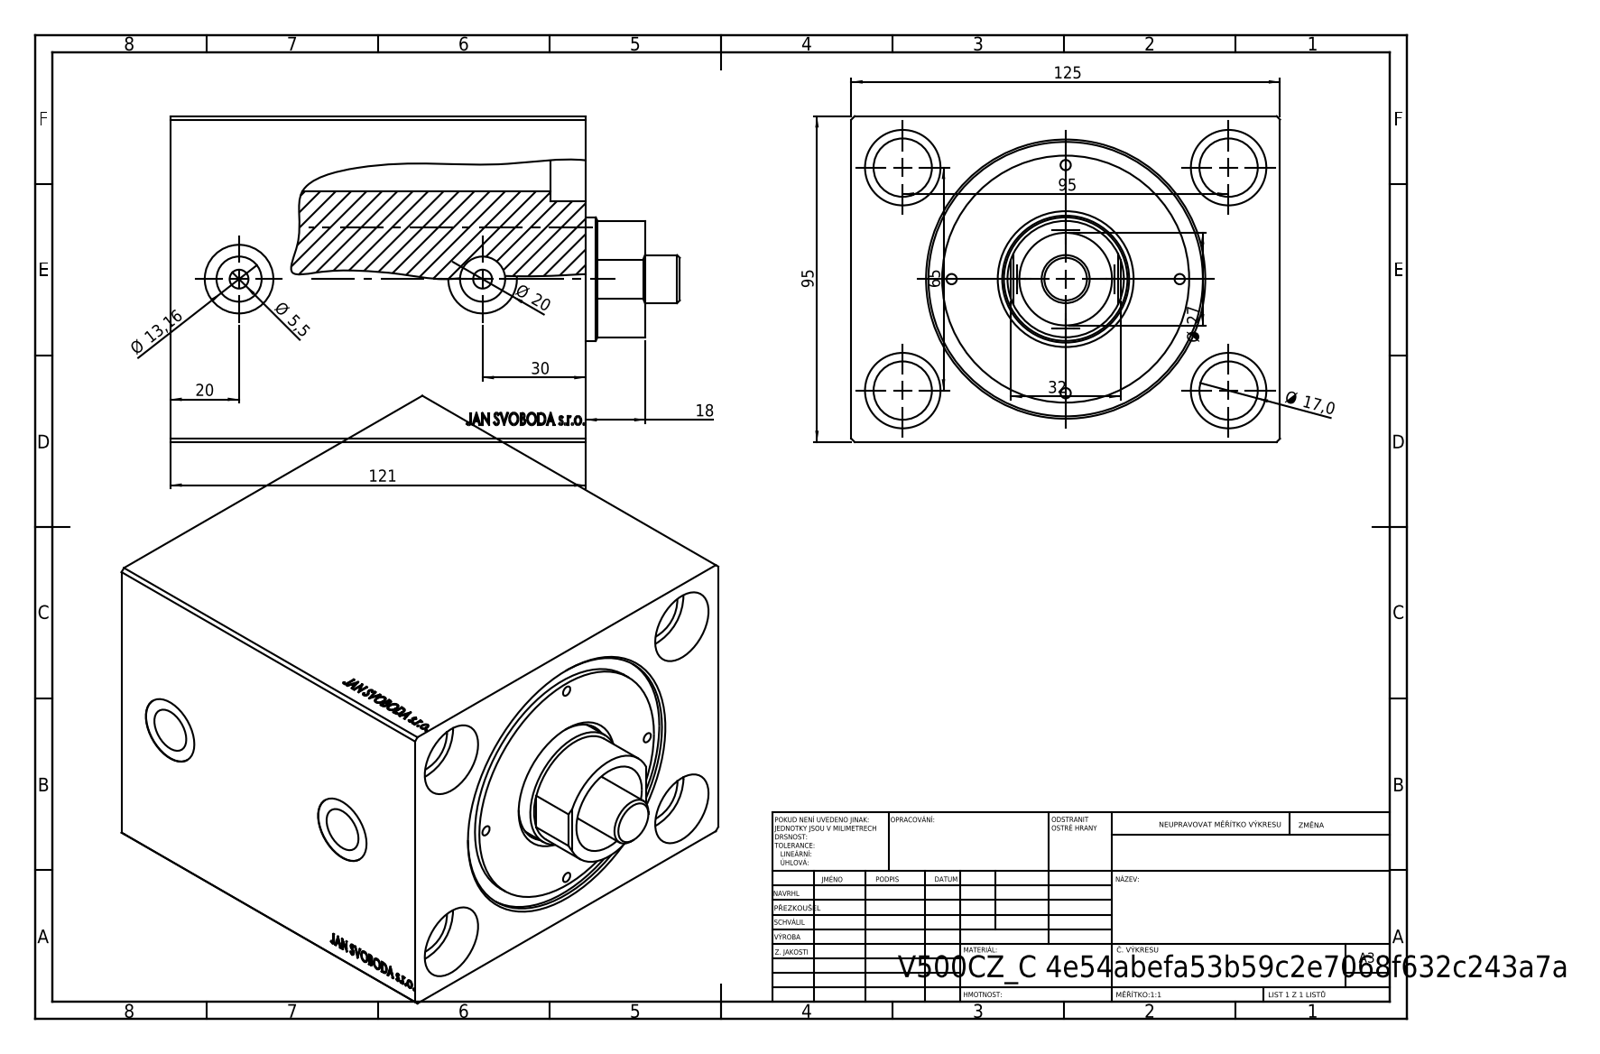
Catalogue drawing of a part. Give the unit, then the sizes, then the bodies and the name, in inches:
Units: inches
Overall size (bounding box): 5.846 × 4.921 × 3.74
Round holes (diameter × count): ⌀0.118 ×4, ⌀0.669 ×4, ⌀0.866 ×4, ⌀0.217 ×2, ⌀0.518 ×2, ⌀0.787 ×2, ⌀1.063 ×1, ⌀1.417 ×1, ⌀1.457 ×1, ⌀2.48 ×1, ⌀3.15 ×1
Round bosses / shafts (diameter × count): ⌀2.835 ×1, ⌀0.551 ×1, ⌀0.472 ×1
Partial cylindrical surfaces — rounded edges, fillets, slot ends (radius × count): R0.668 ×1
Main face-to-face distances: 3.74, 4.921, 4.764, 2.559, 2.205, 0.465, 2.094, 4.299, 0.394, 0.071
Hole centre spacings: 1.309, 1.397, 1.851, 1.87, 2.266, 3.193, 3.427, 2.559
Volume: 76.83 in³ · Surface area: 232 in²
Bodies: 4 solids, 884 faces (411 planar, 71 cylindrical, 402 other)
Part name (STEP PRODUCT): V500CZ_VCP_C; V500CZ_VC_vysunovaci_C; V500CZ_FM; V500CZ_C
STEP written by: SolidWorks 2019 (CONFIG_CONTROL_DESIGN)
